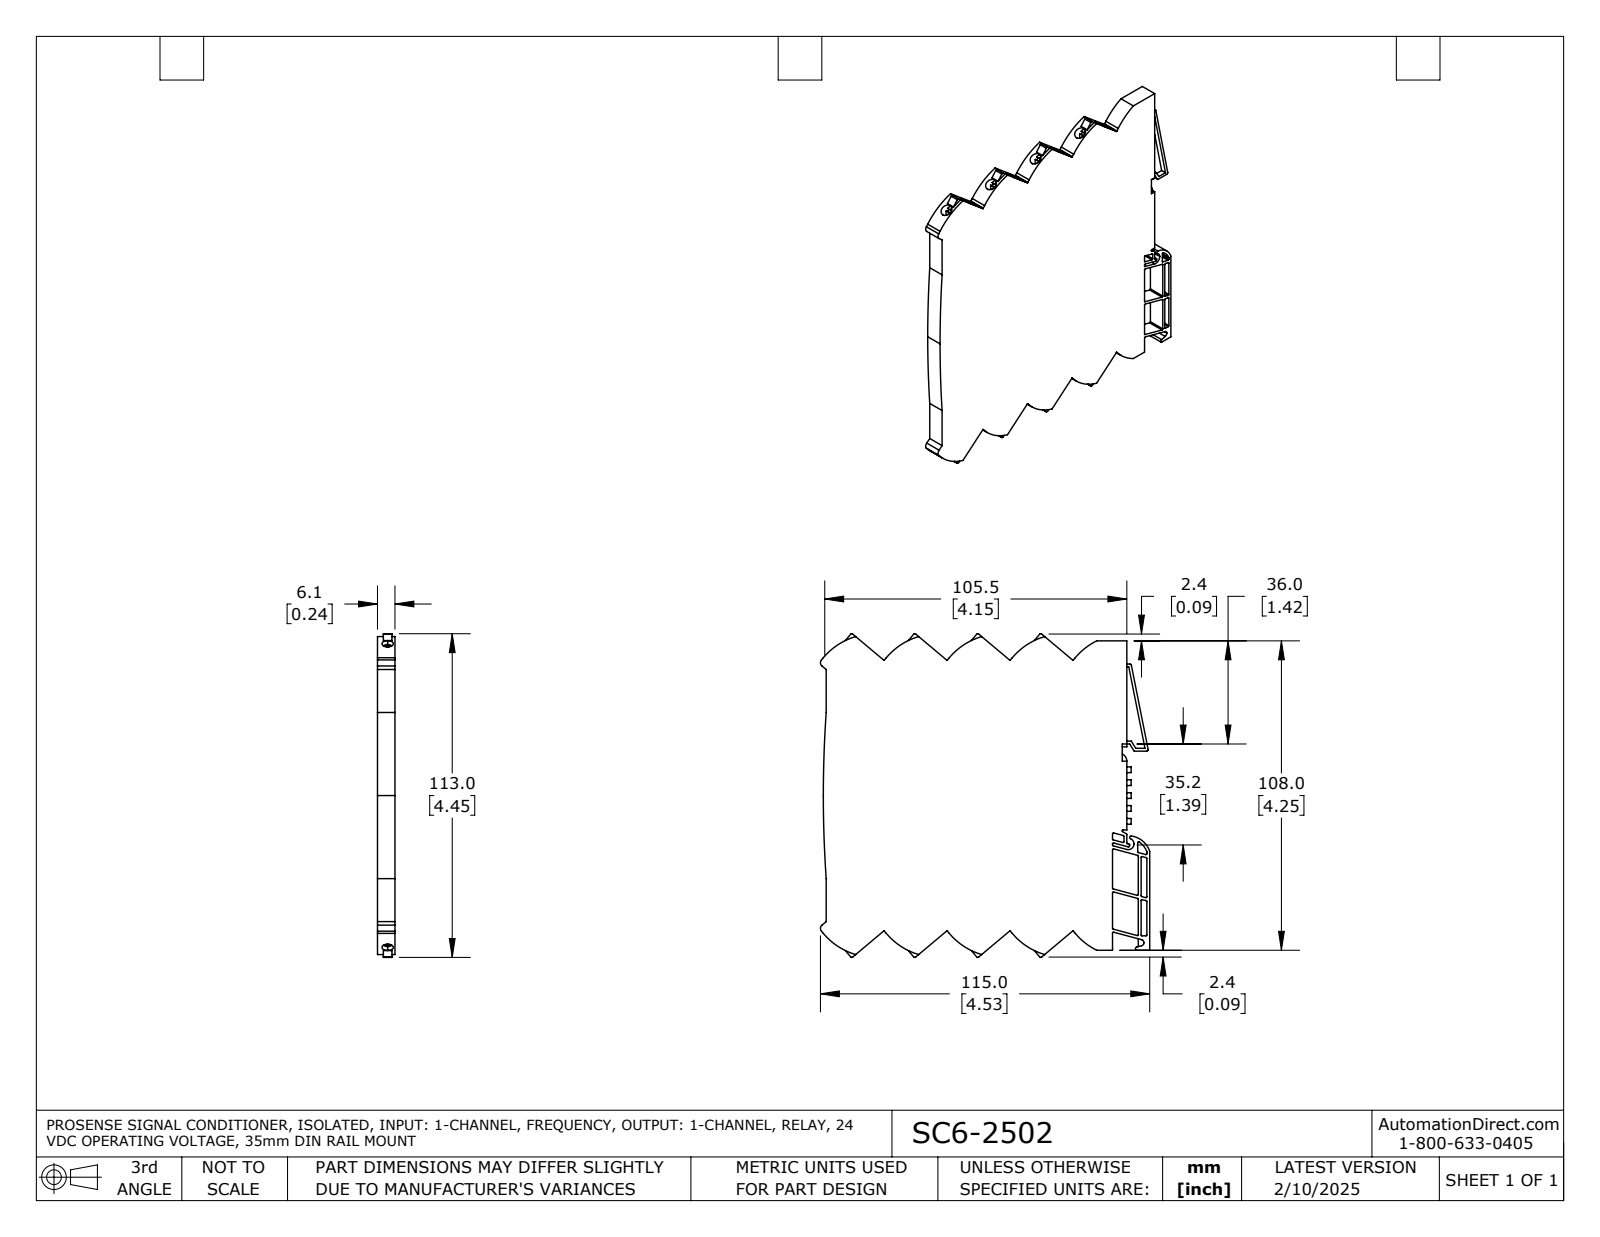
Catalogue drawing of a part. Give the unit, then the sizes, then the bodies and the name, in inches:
Units: inches
Overall size (bounding box): 4.528 × 4.448 × 0.24
Round holes (diameter × count): ⌀0.157 ×8
Partial cylindrical surfaces — rounded edges, fillets, slot ends (radius × count): R0.012 ×32, R0.02 ×11, R0.059 ×10, R0.918 ×10, R0.022 ×1, R0.043 ×1, R0.058 ×1, R0.07 ×1
Main face-to-face distances: 0.24, 0.039, 0.118, 0.157, 0.081, 0.557, 0.159, 0.663, 0.041, 0.079
Hole centre spacings: 0.557, 1.114, 0.557, 1.671
Volume: 3.996 in³ · Surface area: 44.18 in²
Bodies: 1 solid, 457 faces (333 planar, 124 cylindrical, 0 other)
Part name (STEP PRODUCT): SC6-2502
STEP written by: SolidWorks 2021 (AUTOMOTIVE_DESIGN)
